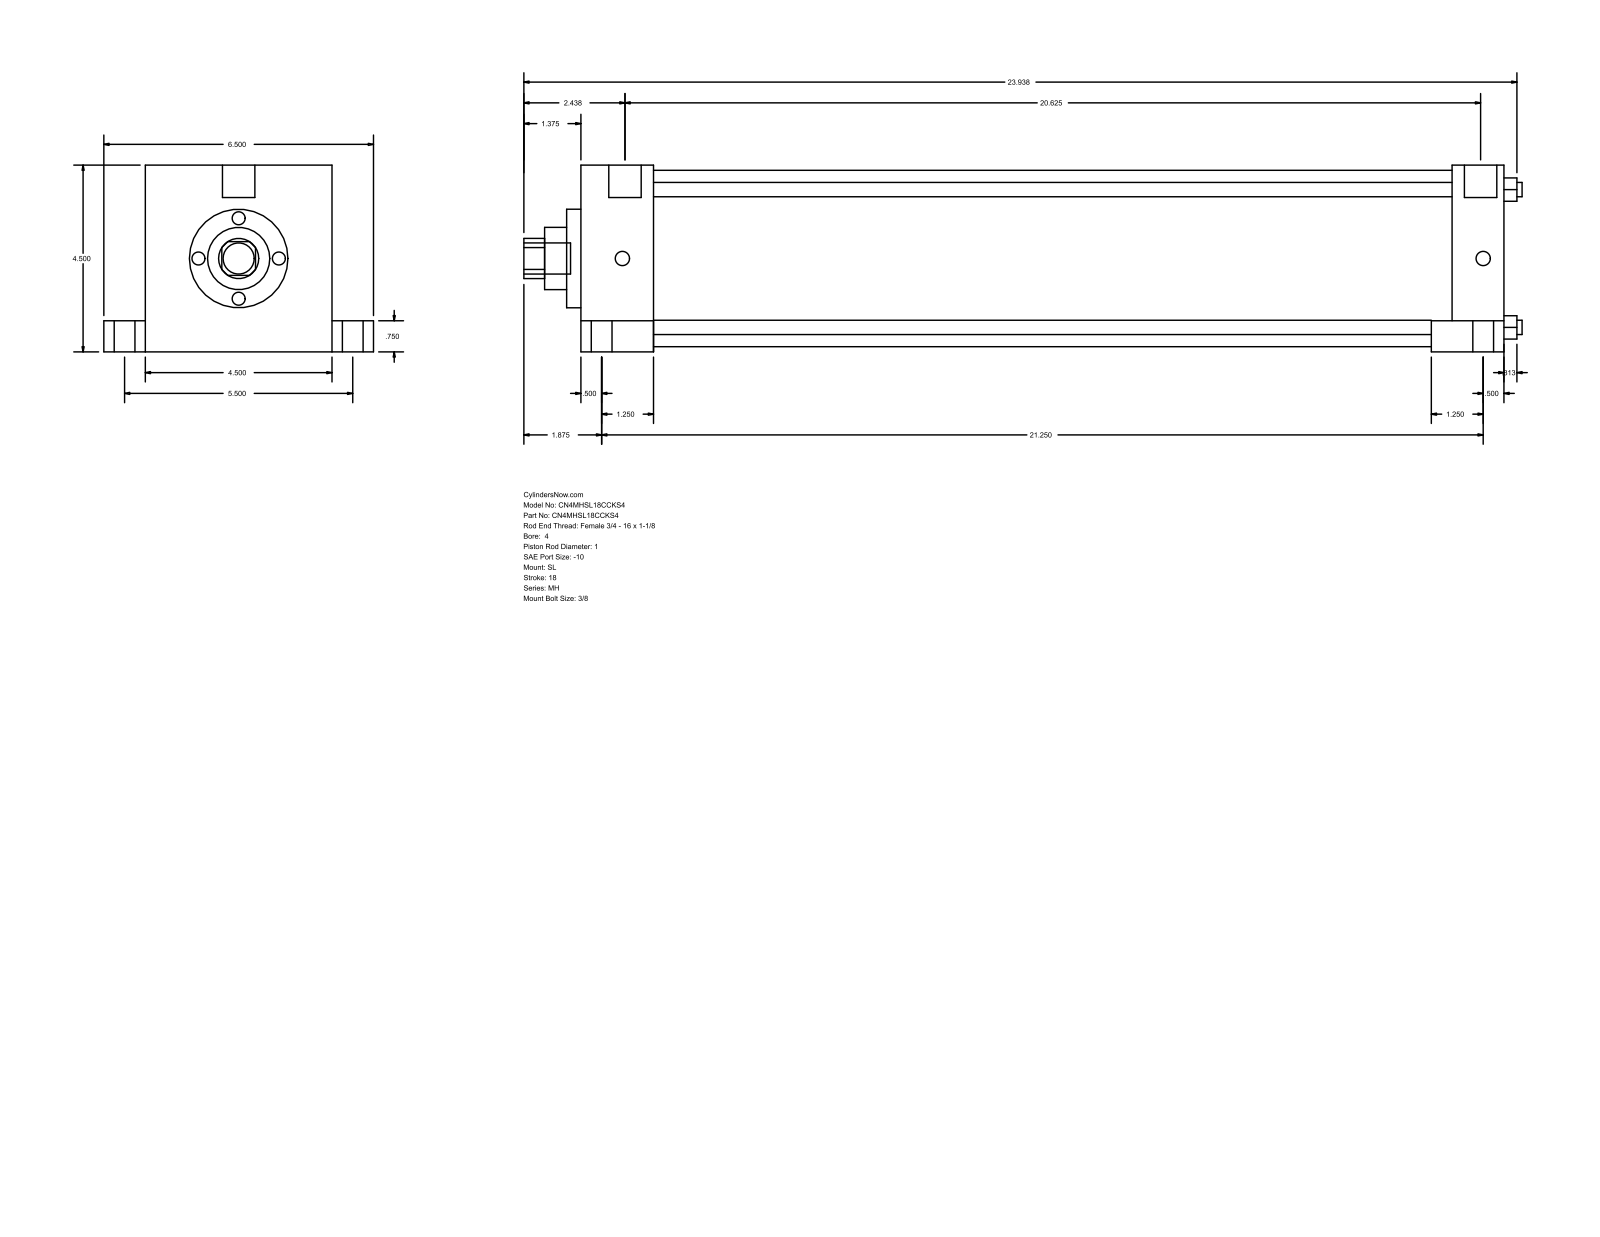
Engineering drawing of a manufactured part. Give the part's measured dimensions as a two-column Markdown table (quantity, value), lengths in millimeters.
| quantity | value |
| --- | --- |
| part name | MH_SL__0400_1 |
| STEP written by | GSSL Pune (CONFIG_CONTROL_DESIGN) |
| units | millimeters |
| bodies | 0 solids, 110 faces (77 planar, 33 cylindrical, 0 other) |
| overall size | 611.19 × 165.1 × 114.3 |
| round holes (diameter × count) | 8.76 × 4, 25.4 × 1, 38.1 × 1, 60.33 × 1, 107.95 × 1 |
| round bosses / shafts (diameter × count) | 19.05 × 5, 12.7 × 4, 8.73 × 4, 19.84 × 2 |
| partial cylindrical surfaces (radius × count) | 12.29 × 1 |
| main face-to-face distances | 114.3, 565.16, 44.46, 520.7, 533.41, 488.95, 31.75, 25.4, 139.7, 19.05 |
| hole center spacings | 59.62, 84.32, 119.25 |
